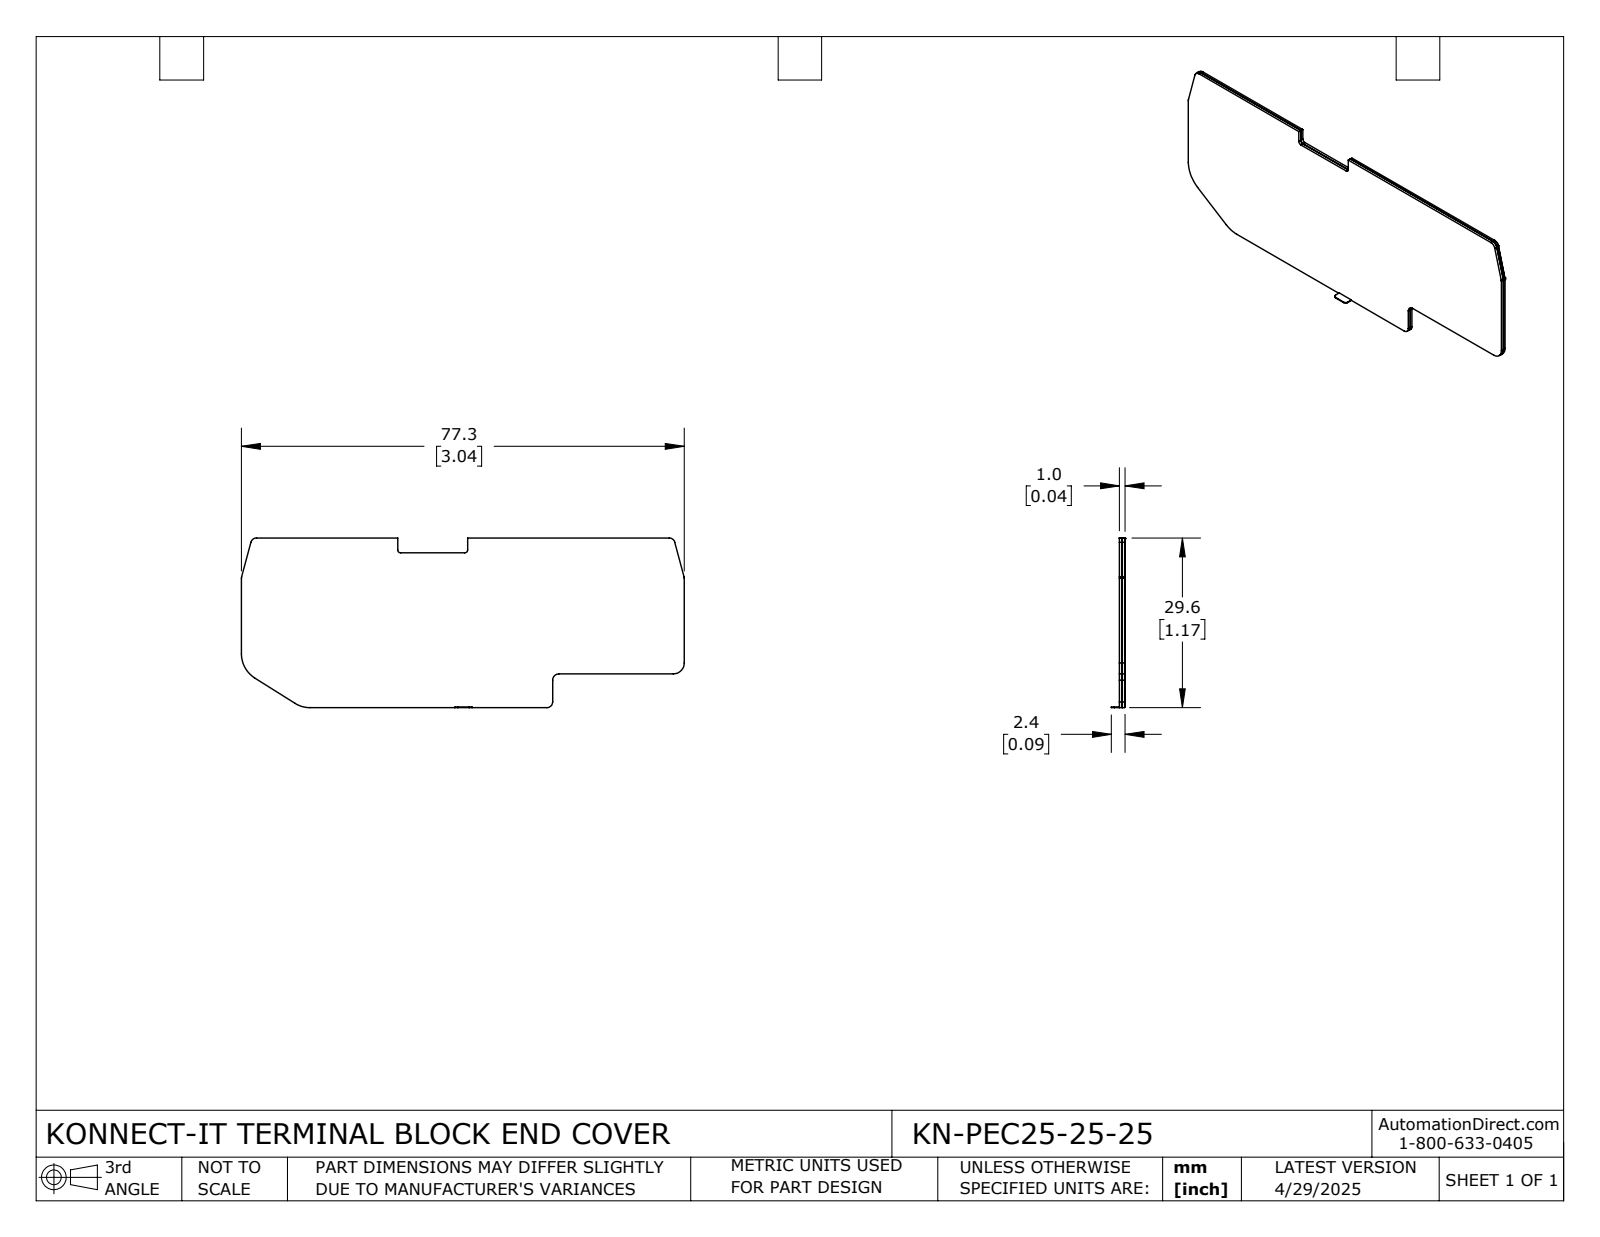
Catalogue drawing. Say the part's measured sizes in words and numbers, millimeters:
The part is named "KN-PEC25-25-25". Its 3-D file was written by "SolidWorks 2024 (CONFIG_CONTROL_DESIGN)". It is 2 solids with 78 faces: 45 planar, 33 cylindrical and 0 other. Overall it measures 77.31 by 29.61 by 2.4 millimeters. Its volume is 2 071 cubic millimeters and its surface area 8 505 square millimeters. Partial cylindrical surfaces (rounded edges, fillets, slot ends): 5 of radius 0.9, 5 of radius 1, 4 of radius 0.5, 2 of radius 4.8, 2 of radius 4.9, 1 of radius 1.1, 1 of radius 1.2, 1 of radius 1.8. The main face-to-face distances are 0.5, 1, 29.61, 5.89, 0.9, 0.4, 23.72, 29.51, 77.31, 27.02.
